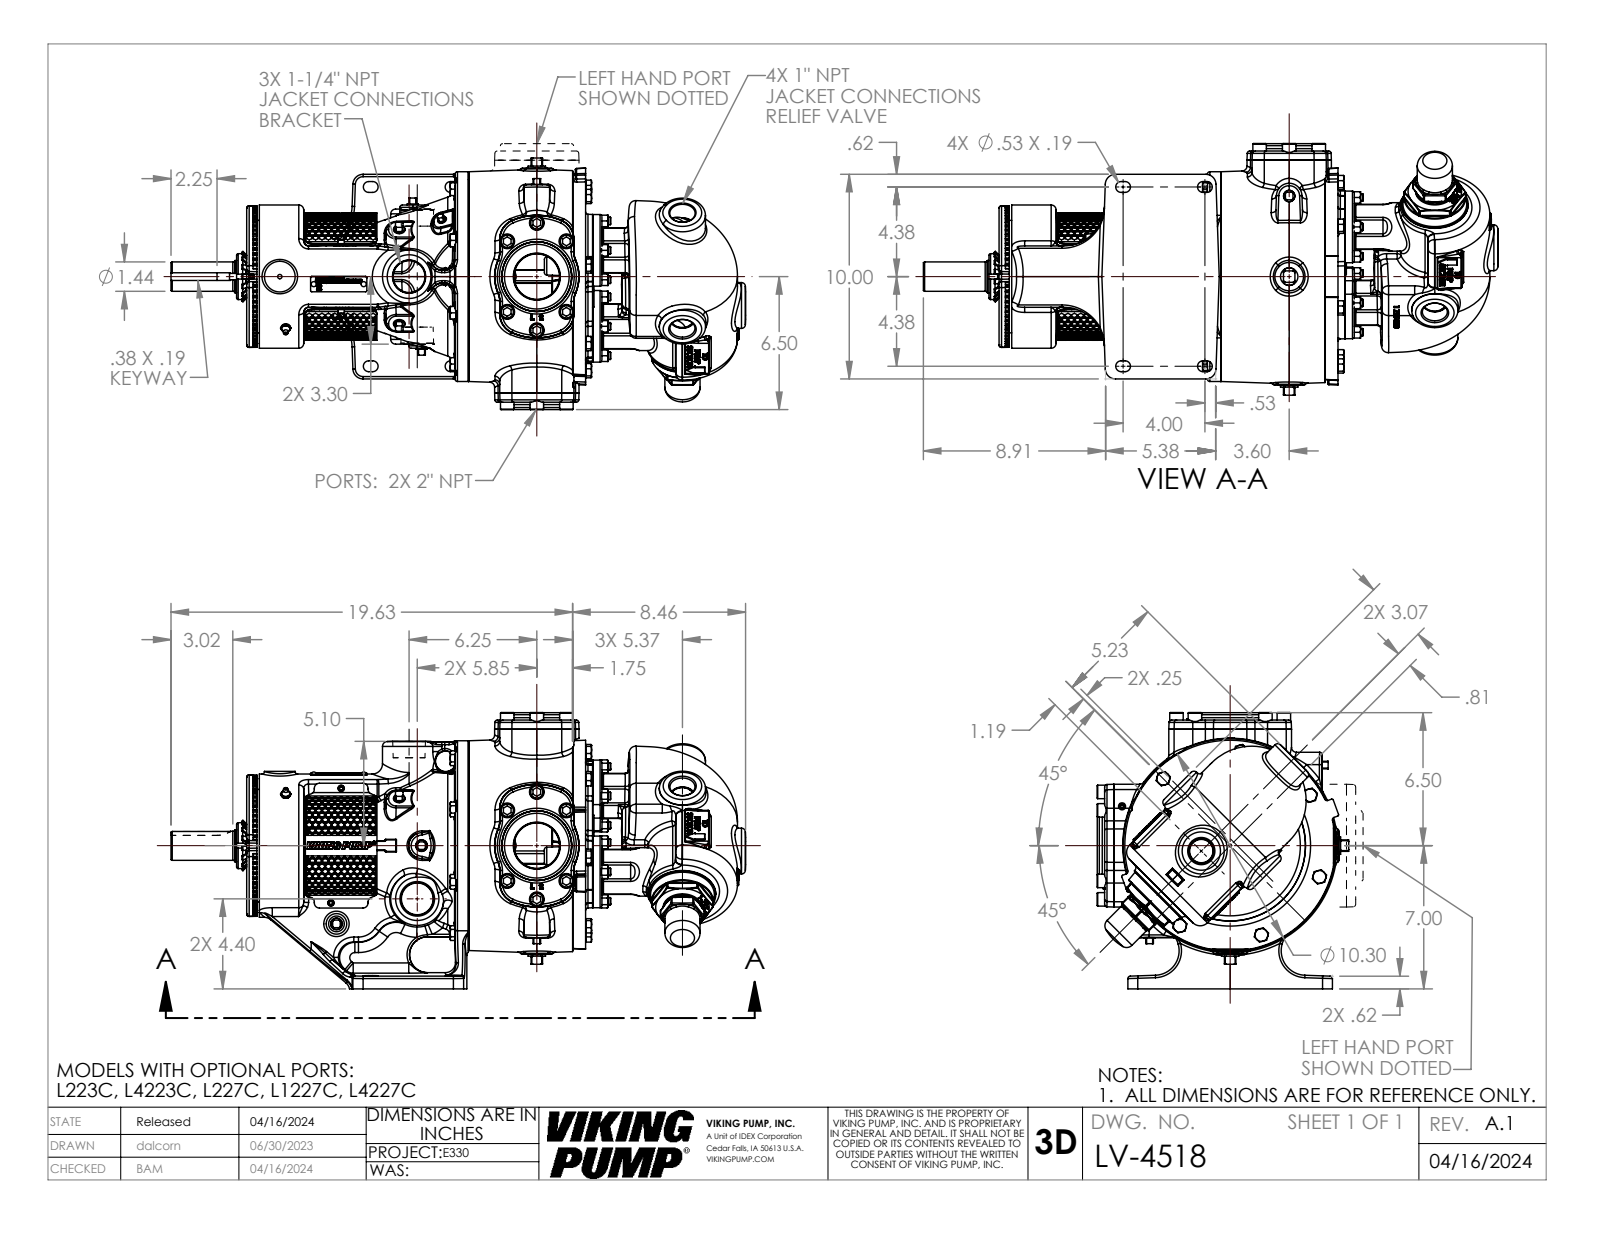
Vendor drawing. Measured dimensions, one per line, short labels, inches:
name: LV-4518
written by: SolidWorks 2024 (AUTOMOTIVE_DESIGN)
unit: in
bodies: 1 solid, 5620 faces (1808 planar, 961 cylindrical, 2851 other)
size: 28.059 × 13.585 × 12.45
volume: 1 157 in³; area: 1 433 in²
holes: 12× ⌀0.719, 8× ⌀1.094, 6× ⌀0.199, 6× ⌀0.25, 3× ⌀0.159, 2× ⌀0.266, 2× ⌀0.313, 1× ⌀0.453, 1× ⌀1.577, 1× ⌀1.593, 1× ⌀2.44, 1× ⌀5.127
bosses: 12× ⌀0.66, 9× ⌀0.625, 8× ⌀0.369, 6× ⌀0.625, 3× ⌀3.5, 3× ⌀0.437, 3× ⌀0.312, 1× ⌀10.25
rounds: 109× R0.063, 86× R0.12, 74× R0.069, 34× R0.03, 34× R0.5, 26× R0.01, 16× R0.24, 16× R1
face distances: 2.25, 13.792, 3.537, 10.255, 2.75, 0.5, 2.143, 5.68, 15.935, 1
hole spacings: 3, 1.375, 2.18, 3.609, 4.446, 4.583, 4.625, 6.404
